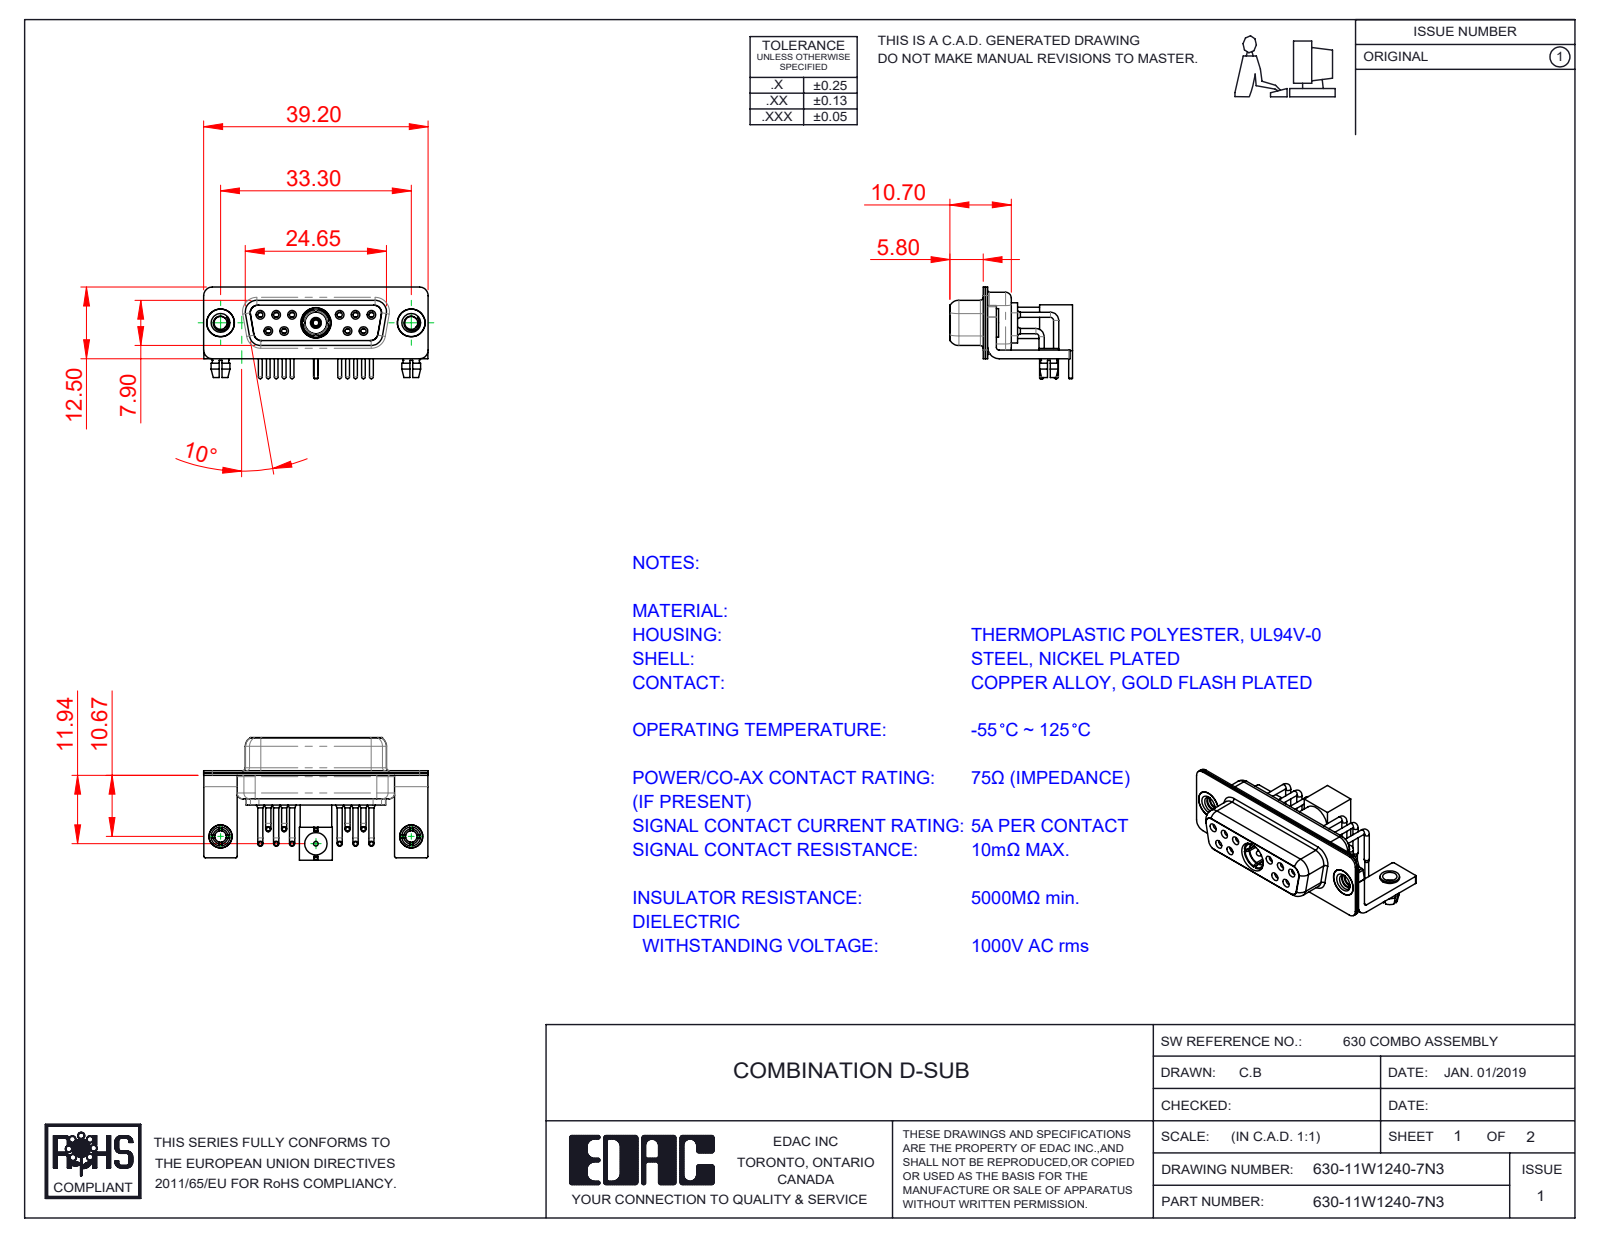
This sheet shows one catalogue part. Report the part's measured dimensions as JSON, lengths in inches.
{"part_name": "RA Back Shell; Insulator RA Pin; 630Combo Contact Row 1; 630Combo Board Lock (+8 more)", "step_written_by": "SolidWorks 2020 (CONFIG_CONTROL_DESIGN)", "units": "inches", "bodies": {"solids": 25, "faces": 1109, "planar": 352, "cylindrical": 482, "other": 275}, "overall_size": [1.543, 0.843, 0.63], "volume_in3": 0.19, "surface_area_in2": 11.92, "round_holes": [[0.079, 12], [0.043, 11], [0.059, 11], [0.035, 10], [0.067, 6], [0.063, 4], [0.191, 3], [0.089, 2], [0.098, 2], [0.126, 2], [0.157, 2], [0.159, 2]], "round_bosses_or_shafts": [[0.035, 10], [0.026, 10], [0.063, 6], [0.197, 3], [0.157, 3], [0.114, 3], [0.195, 2], [0.189, 2]], "partial_cylinders_radius": [[0.01, 16], [0.059, 16], [0.079, 13], [0.053, 12], [0.063, 8], [0.02, 5], [0.024, 4], [0.026, 4]], "face_to_face_distances": [0.016, 0.031, 0.055, 0.018, 0.071, 0.333, 0.059, 0.35, 0.244, 0.091], "hole_center_spacings": [0.124, 0.109, 0.545, 0.436, 0.654, 0.198, 0.198, 0.218]}
